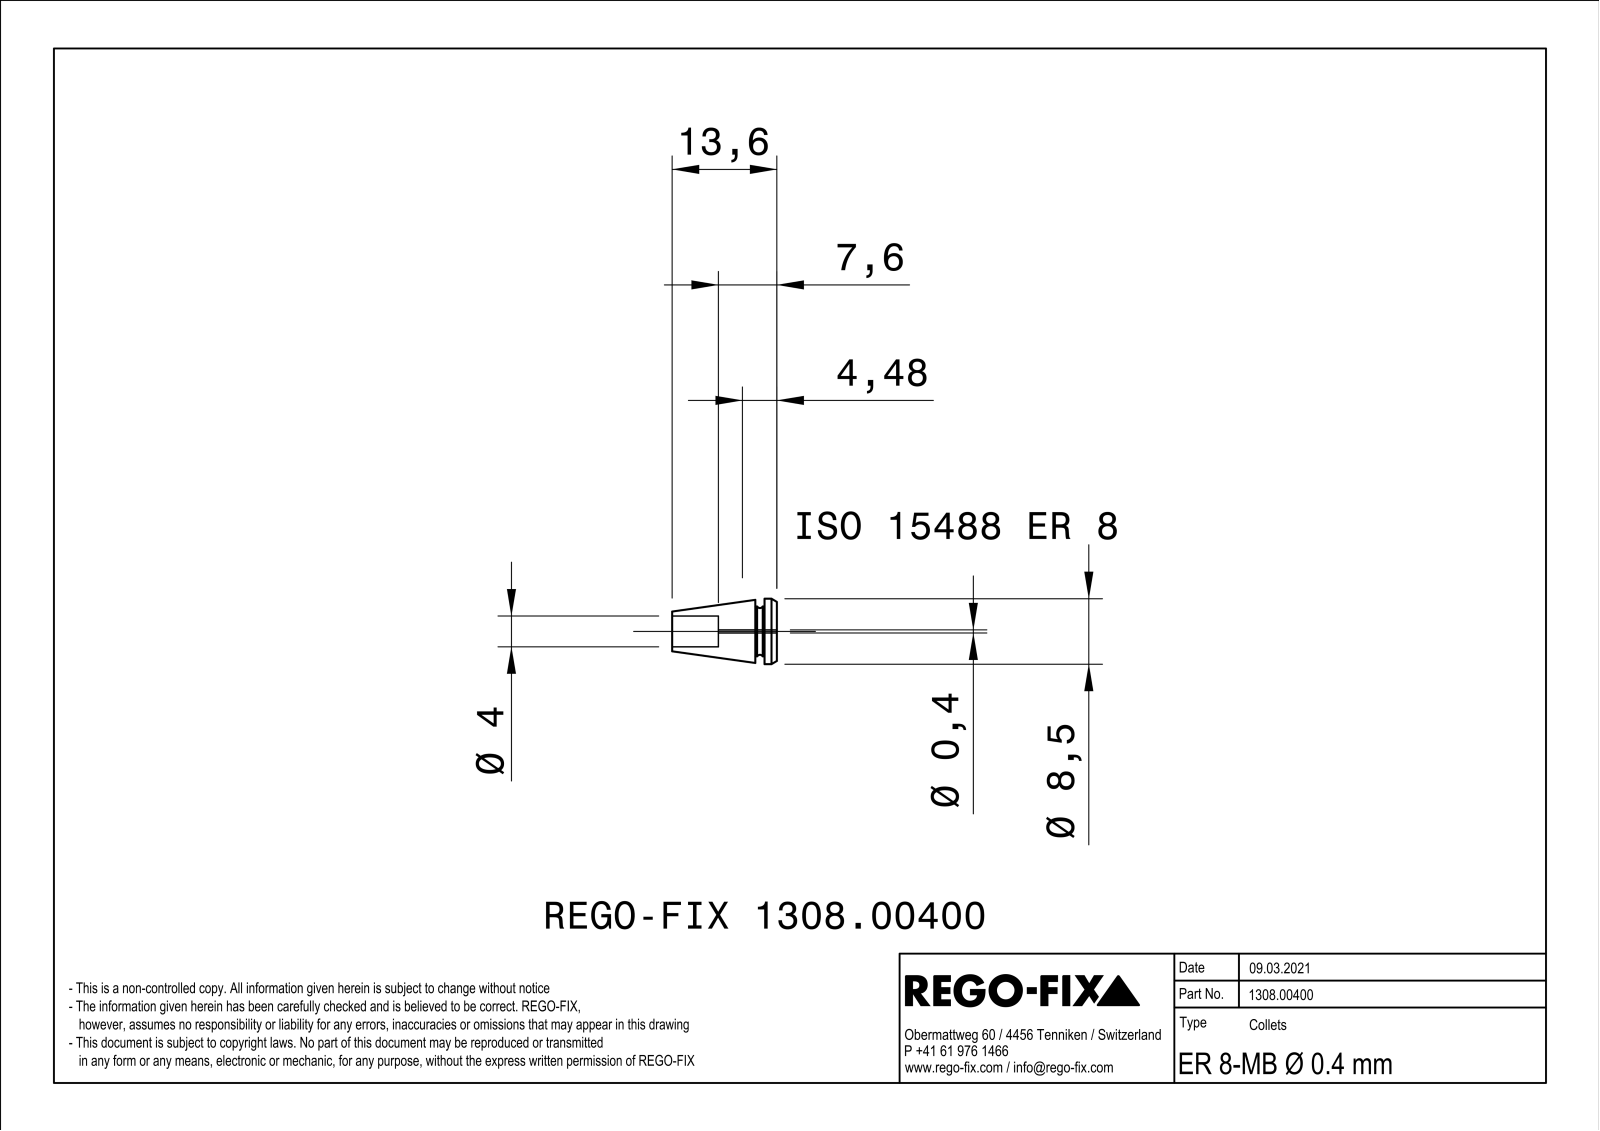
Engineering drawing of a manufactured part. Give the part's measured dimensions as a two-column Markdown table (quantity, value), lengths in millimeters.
| quantity | value |
| --- | --- |
| part name | NOCUT |
| STEP written by | SIEMENS PLM Software Solid Edge ST10 (AUTOMOTIVE_DESIGN) |
| units | millimeters |
| bodies | 1 solid, 83 faces (27 planar, 25 cylindrical, 31 other) |
| overall size | 13.6 × 8.5 × 8.49 |
| volume | 357 mm³ |
| surface area | 722 mm² |
| round holes (diameter × count) | 1.2 × 3, 4 × 1 |
| round bosses / shafts (diameter × count) | 8.5 × 1, 6.5 × 1 |
| partial cylindrical surfaces (radius × count) | 25 × 3, 0.2 × 1 |
| main face-to-face distances | 0.6, 0.41, 1.6, 2.8, 1.2, 6, 7.6, 4.8, 11.2, 9.6 |
| hole center spacings | 1.35, 2.34 |
